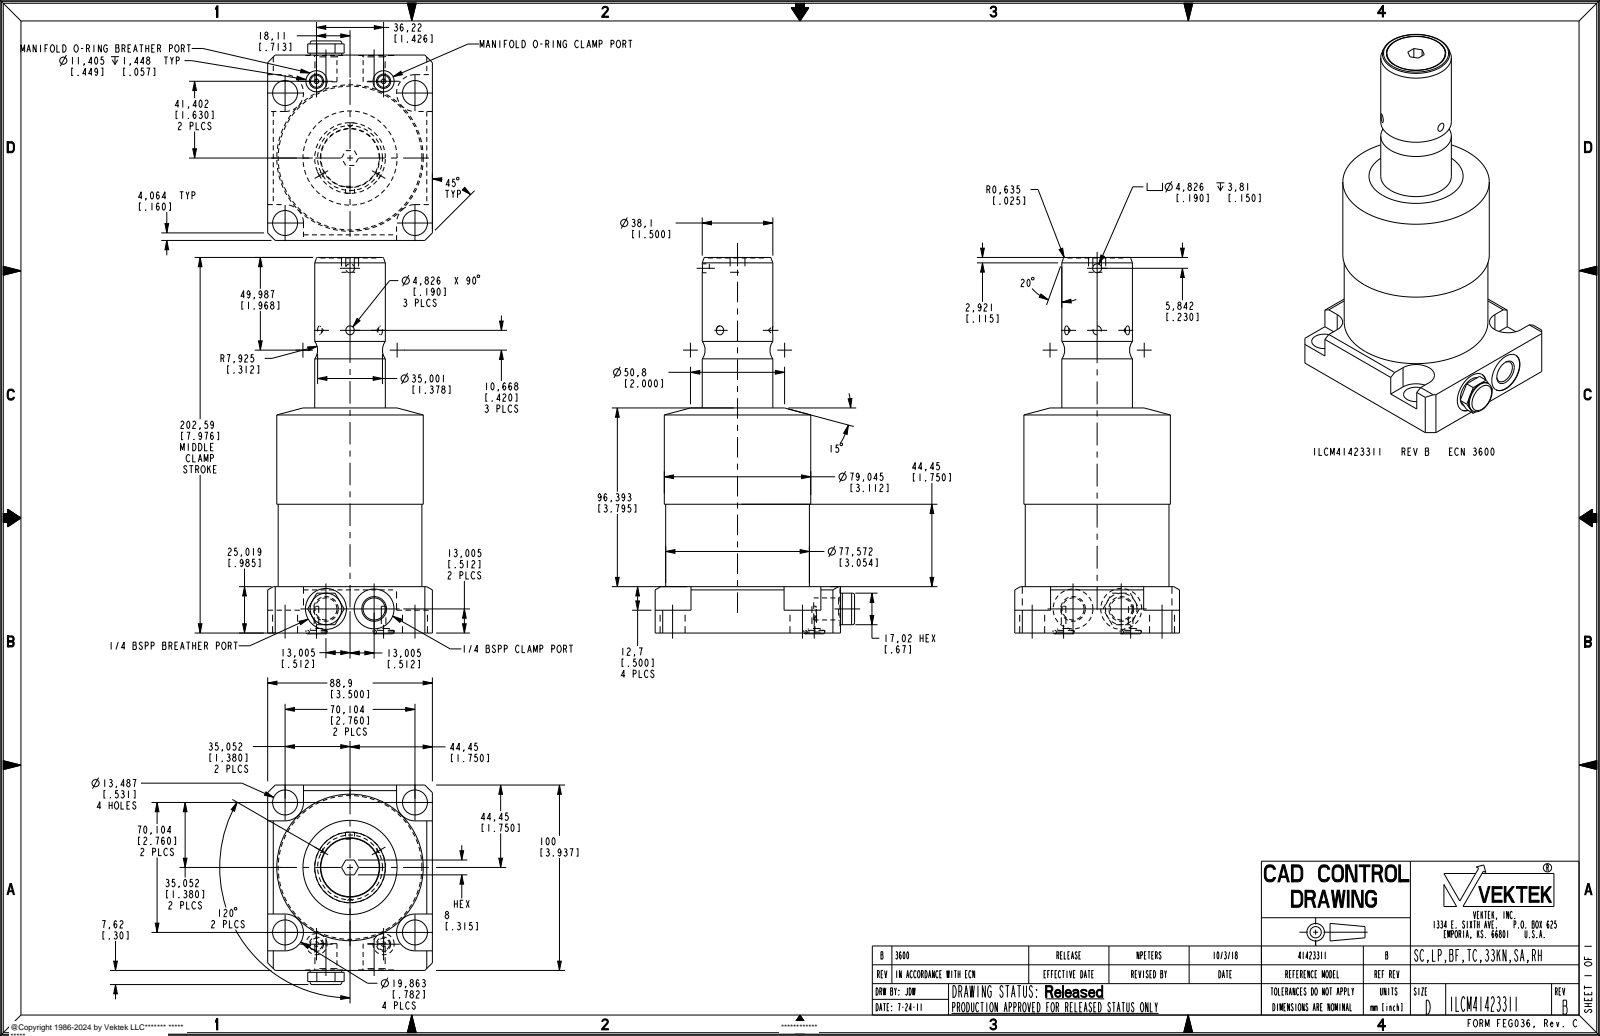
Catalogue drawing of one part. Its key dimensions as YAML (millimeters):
part_name: "ILCM41423311"
step_written_by: "PRO/ENGINEER BY PARAMETRIC TECHNOLOGY CORPORATION, 2013320 (AUTOMOTIVE_DESIGN)"
units: millimeters
bodies: {solids: 1, faces: 150, planar: 70, cylindrical: 52, other: 28}
overall_size: [203, 107.62, 88.9]
volume: 744722
surface_area: 64000
round_holes:
  - {diameter: 13.49, count: 4}
  - {diameter: 2.49, count: 2}
  - {diameter: 6.5, count: 2}
  - {diameter: 11.4, count: 2}
  - {diameter: 11.89, count: 2}
  - {diameter: 4.83, count: 1}
  - {diameter: 21.49, count: 1}
  - {diameter: 22.1, count: 1}
  - {diameter: 32, count: 1}
round_bosses_or_shafts:
  - {diameter: 79.05, count: 1}
  - {diameter: 77.57, count: 1}
  - {diameter: 38.1, count: 1}
  - {diameter: 31.5, count: 1}
  - {diameter: 17.02, count: 1}
partial_cylinders:
  - {radius: 9.93, count: 4}
face_to_face_distances: [25.02, 88.9, 100, 96.39, 121.41, 81.18, 177.57, 202.59, 190.27, 109.09]
hole_center_spacings: [49.57, 70.1, 18.09, 45.19, 53.54, 78.3, 93.12, 99.14]
